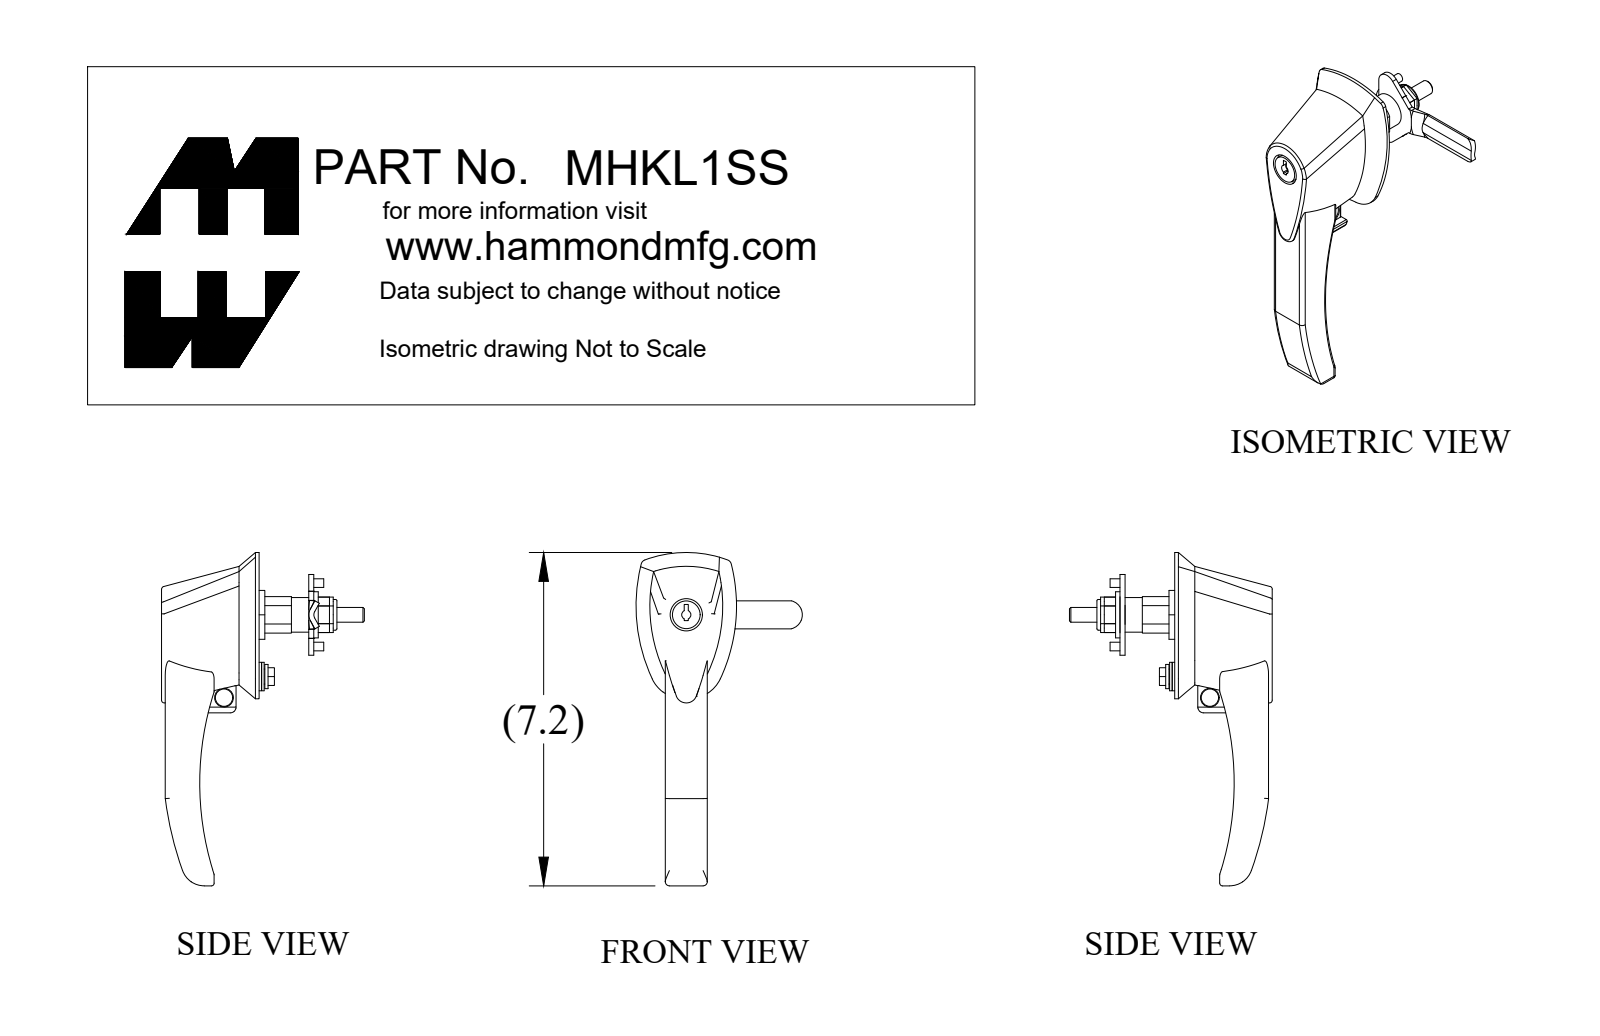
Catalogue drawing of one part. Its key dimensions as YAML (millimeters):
part_name: "MHKL1SS"
step_written_by: "SolidWorks 2018 (AUTOMOTIVE_DESIGN)"
units: millimeters
bodies: {solids: 10, faces: 252, planar: 120, cylindrical: 87, other: 45}
overall_size: [183.5, 111.7, 91.6]
volume: 181900
surface_area: 38560
round_holes:
  - {diameter: 5.9, count: 1}
  - {diameter: 8.5, count: 1}
  - {diameter: 8.9, count: 1}
  - {diameter: 9.5, count: 1}
  - {diameter: 11.1, count: 1}
  - {diameter: 11.3, count: 1}
  - {diameter: 17.8, count: 1}
  - {diameter: 19.2, count: 1}
round_bosses_or_shafts:
  - {diameter: 4.7, count: 2}
  - {diameter: 25.4, count: 1}
  - {diameter: 19.1, count: 1}
  - {diameter: 16.9, count: 1}
  - {diameter: 15.7, count: 1}
  - {diameter: 15.2, count: 1}
  - {diameter: 13.3, count: 1}
  - {diameter: 8.3, count: 1}
partial_cylinders:
  - {radius: 0.8, count: 6}
  - {radius: 2.3, count: 6}
  - {radius: 1.5, count: 5}
  - {radius: 3.2, count: 3}
  - {radius: 6.4, count: 3}
  - {radius: 19.1, count: 2}
  - {radius: 94.5, count: 2}
  - {radius: 2.5, count: 1}
face_to_face_distances: [23.1, 30.1, 83.9, 53.7, 81.8, 51.7, 2, 81.1, 2.8, 27.4]
hole_center_spacings: [34]
